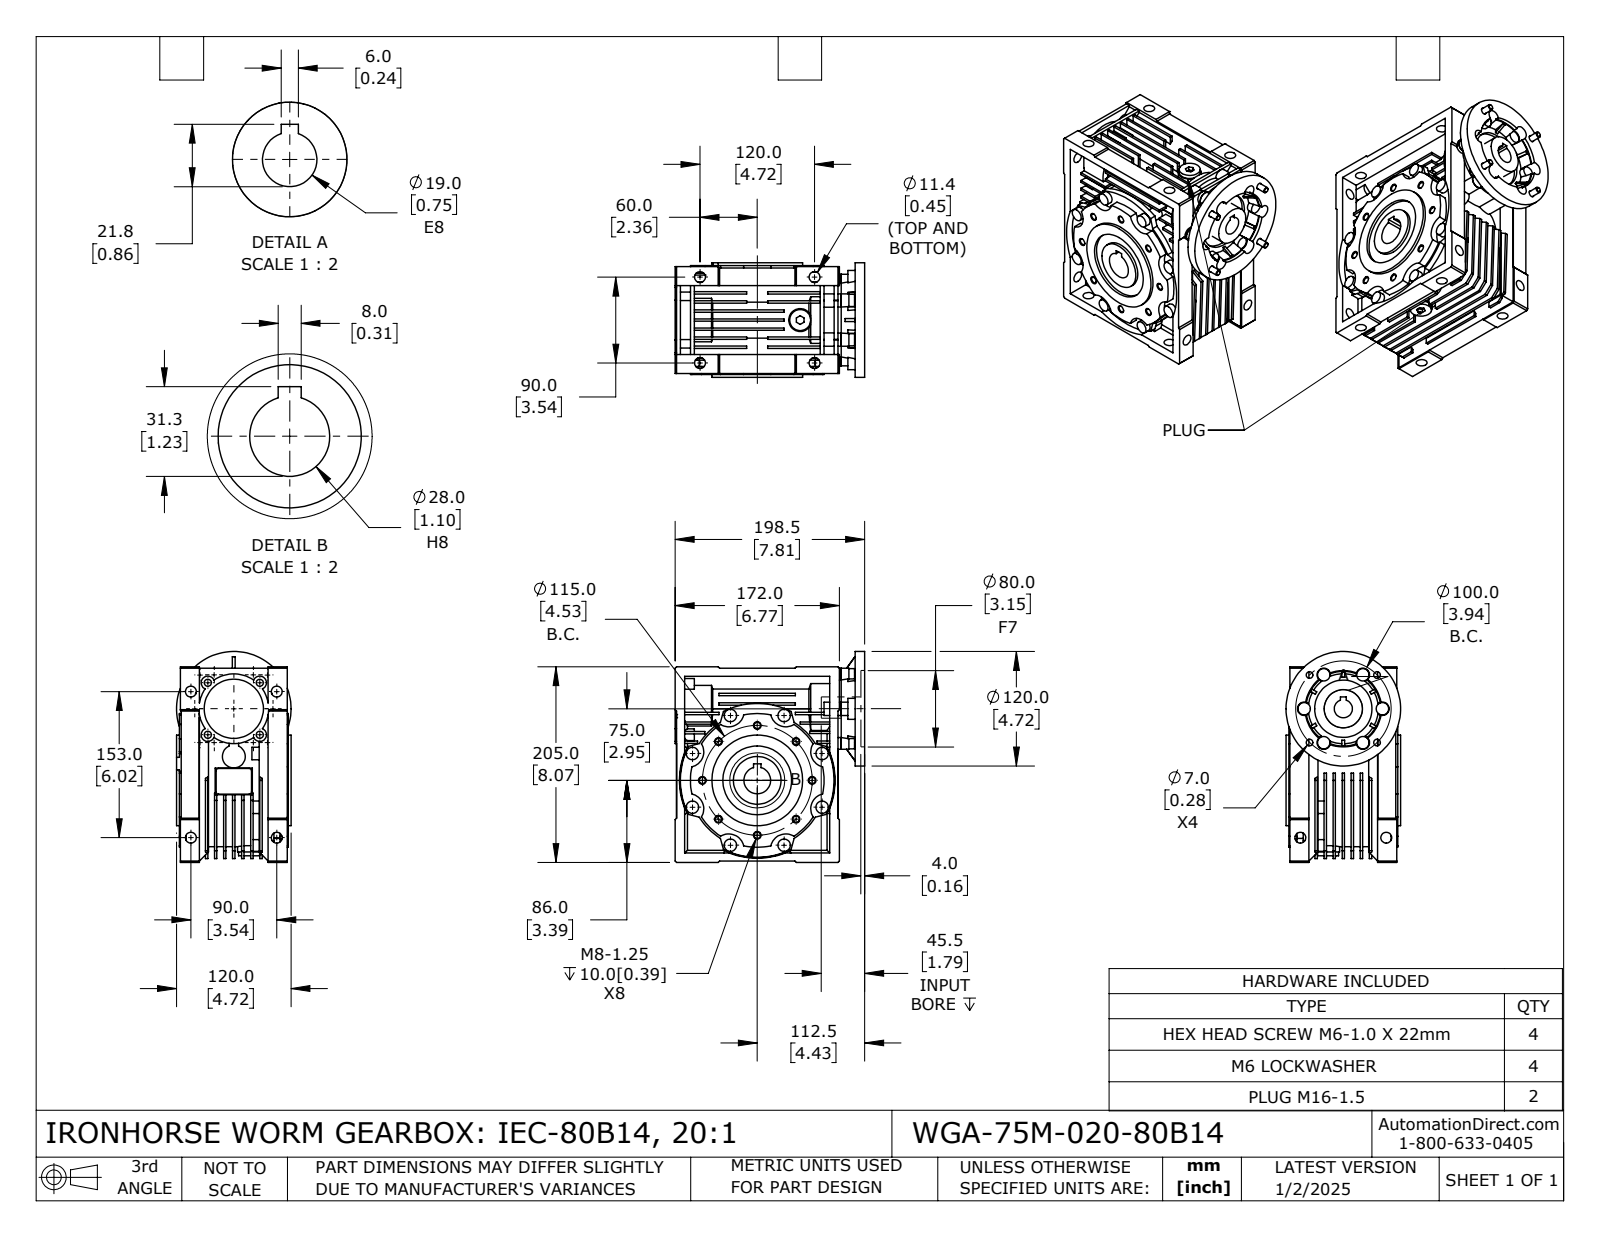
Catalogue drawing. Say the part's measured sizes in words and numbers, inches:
The part is named "WGA-75M-020-80B14". Its 3-D file was written by "SolidWorks 2024 (CONFIG_CONTROL_DESIGN)". It is 16 solids with 1304 faces: 703 planar, 433 cylindrical and 168 other. Overall it measures 8.701 by 8.228 by 4.724 inches. Its volume is 174.1 cubic inches and its surface area 745.4 square inches. Round holes: 8 of diameter 0.262, 8 of diameter 0.448, 4 of diameter 0.24, 4 of diameter 0.276, 4 of diameter 0.293, 2 of diameter 0.571, 1 of diameter 0.748, 1 of diameter 0.787, 1 of diameter 1.102, 1 of diameter 1.535, 1 of diameter 1.654, 1 of diameter 1.969. Round bosses or shafts: 14 of diameter 0.512, 4 of diameter 0.48, 4 of diameter 0.236, 3 of diameter 0.945, 2 of diameter 0.866, 2 of diameter 0.622, 2 of diameter 0.539, 1 of diameter 5.509. Partial cylindrical surfaces (rounded edges, fillets, slot ends): 10 of radius 0.276, 8 of radius 0.63, 6 of radius 0.433, 4 of radius 0.098, 1 of radius 1.417, 1 of radius 1.437, 1 of radius 1.535, 1 of radius 1.575. The main face-to-face distances are 0.374, 0.098, 0.748, 0.472, 0.394, 0.276, 0.65, 1.122, 1.093, 0.846. The hole center spacings are 1.733, 2.264, 2.485, 3.202, 4.183, 0.453, 1.515, 1.969.
